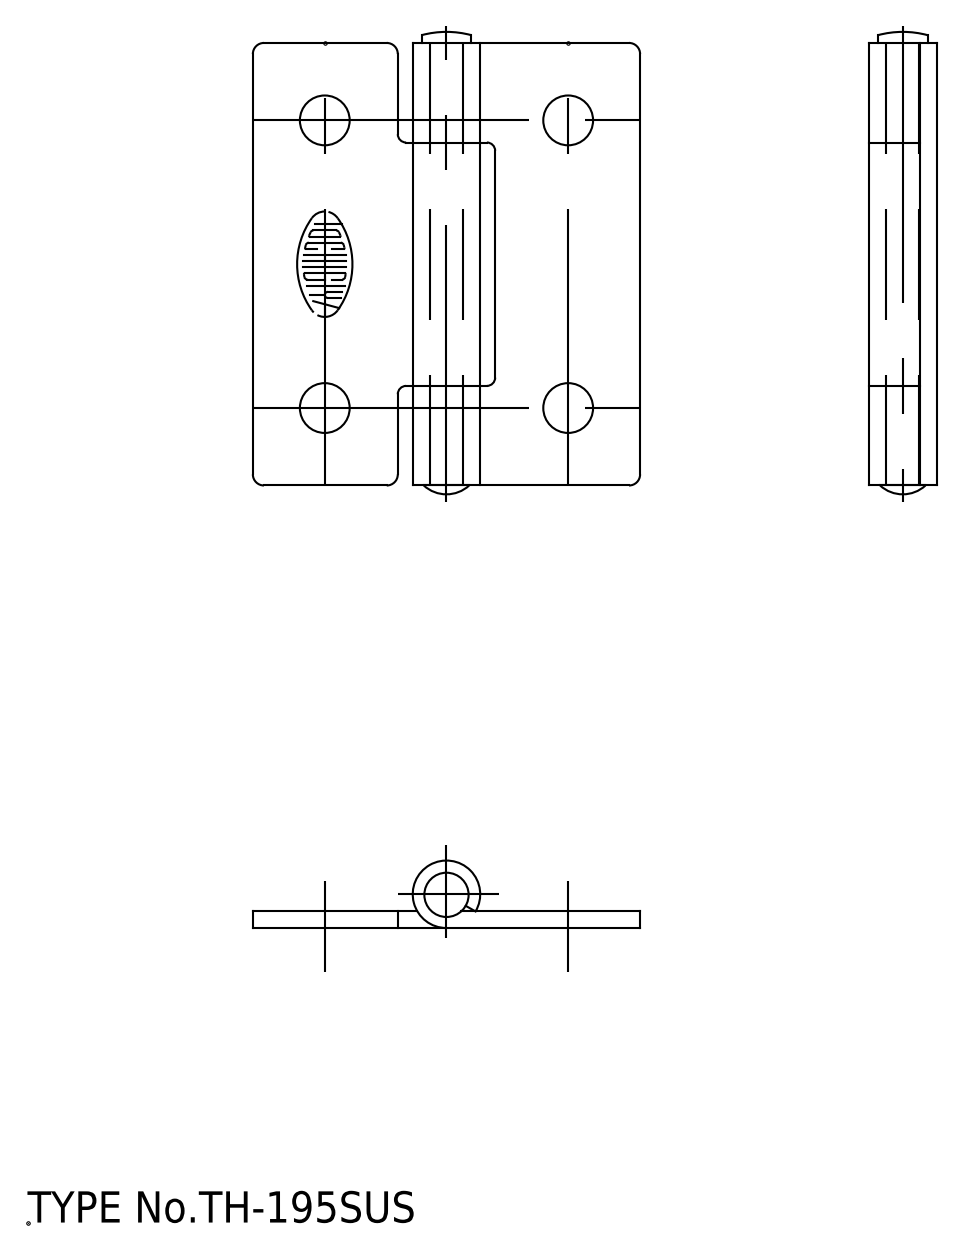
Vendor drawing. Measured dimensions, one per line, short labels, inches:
name: シャフト; ヒンジピース(A); ヒンジピース(B)
written by: spGate 19.8.4 (****-****-****-****) (AUTOMOTIVE_DESIGN)
unit: in
bodies: 3 solids, 57 faces (22 planar, 31 cylindrical, 4 other)
size: 1.646 × 1.378 × 0.24
volume: 0.169 in³; area: 6.608 in²
holes: 4× ⌀0.177, 1× ⌀0.122
bosses: 1× ⌀0.24, 1× ⌀0.177, 1× ⌀0.118
rounds: 6× R0.039, 4× R0.03, 2× R0.004
face distances: 0.059, 0.354, 1.22, 1.575, 1.378, 0.516, 0.862, 0.866, 0.346
hole spacings: 0.866, 1.024, 1.341
